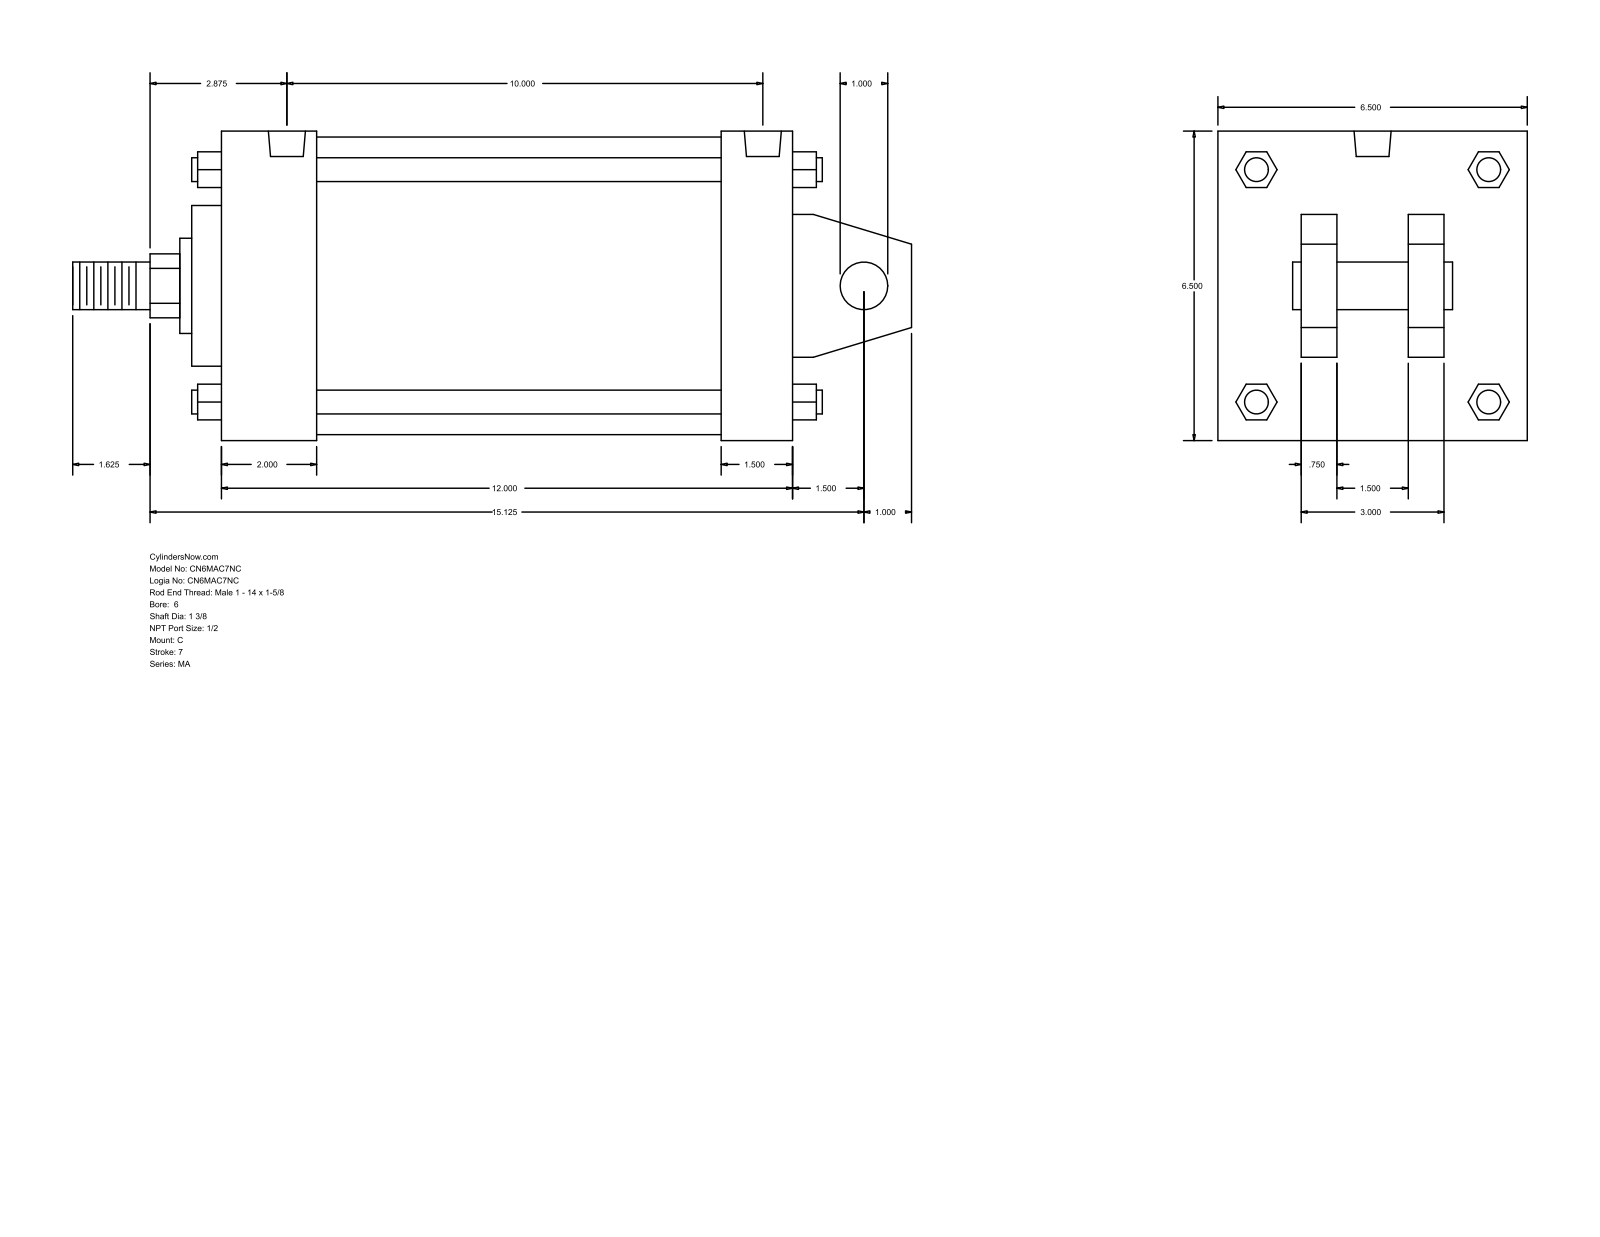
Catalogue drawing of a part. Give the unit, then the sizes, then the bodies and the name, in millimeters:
Units: millimetres
Overall size (bounding box): 447.68 × 165.1 × 165.1
Round holes (diameter × count): ⌀17.46 ×4, ⌀19.77 ×2
Round bosses / shafts (diameter × count): ⌀12.7 ×4, ⌀25.4 ×2, ⌀158.75 ×1, ⌀85.72 ×1, ⌀50.8 ×1, ⌀34.92 ×1
Partial cylindrical surfaces — rounded edges, fillets, slot ends (radius × count): R17.06 ×1
Main face-to-face distances: 165.1, 304.8, 38.1, 19.05, 63.5, 101.6, 50.8, 120.65, 44.45, 266.7
Hole centre spacings: 254, 3.17, 3.18, 250.82, 253.99, 257.17
Bodies: 0 solids, 141 faces (109 planar, 32 cylindrical, 0 other)
Part name (STEP PRODUCT): MA_C__0600_1.375
STEP written by: GSSL Pune (CONFIG_CONTROL_DESIGN)
